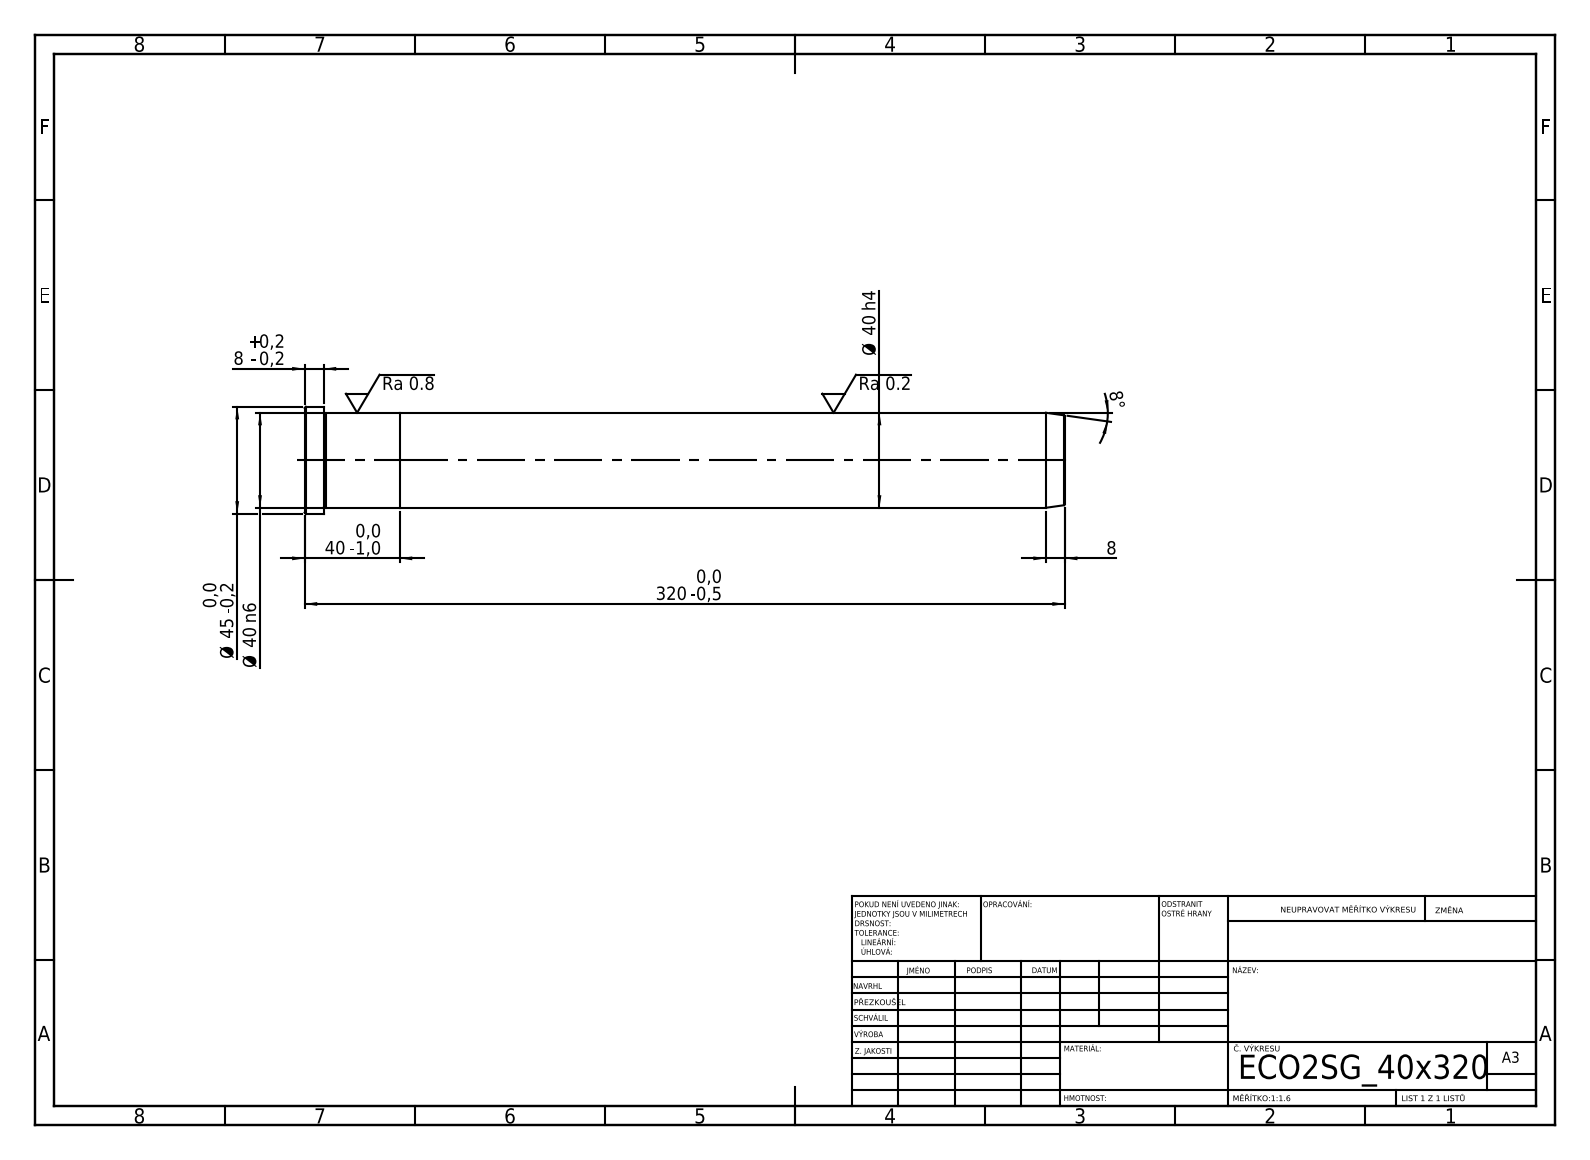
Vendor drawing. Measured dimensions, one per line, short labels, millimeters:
written by: SolidWorks 2019 (CONFIG_CONTROL_DESIGN)
unit: mm
bodies: 2 solids, 21 faces (5 planar, 6 cylindrical, 10 other)
size: 320 × 45 × 45
volume: 404 169 mm³; area: 45 885 mm²
bosses: 1× ⌀45, 1× ⌀40
face distances: 40, 280, 320, 312, 32, 8
